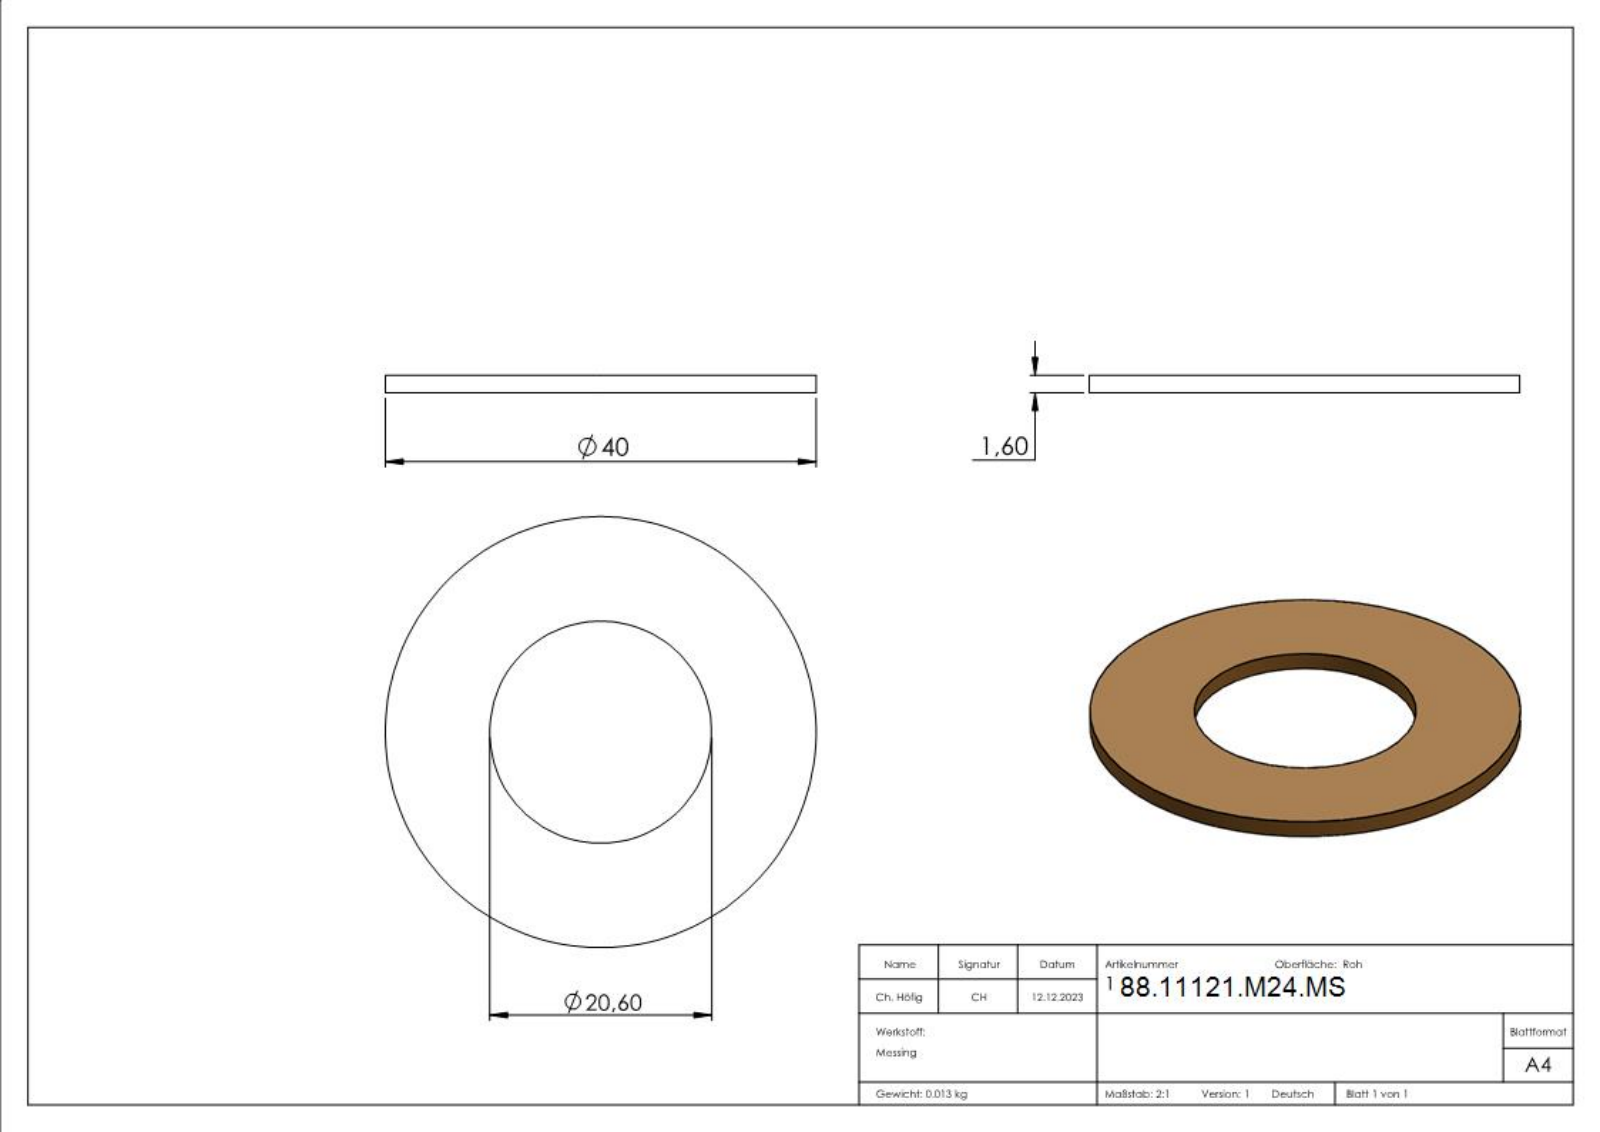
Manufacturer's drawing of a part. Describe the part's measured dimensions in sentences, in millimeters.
The part is named "121-M24-MS". Its 3-D file was written by "SolidWorks 2018 (CONFIG_CONTROL_DESIGN)". It is 1 solid with 271 faces: 174 planar, 2 cylindrical and 95 other. Overall it measures 40 by 40 by 1.6 millimeters. Its volume is 1 477 cubic millimeters and its surface area 2 160 square millimeters. Round holes: 1 of diameter 20.6. Round bosses or shafts: 1 of diameter 40. The main face-to-face distances are 1.6, 1.5, 0.32, 2.32, 2.57, 0.34, 2.45, 2.2, 28.06, 1.15.
